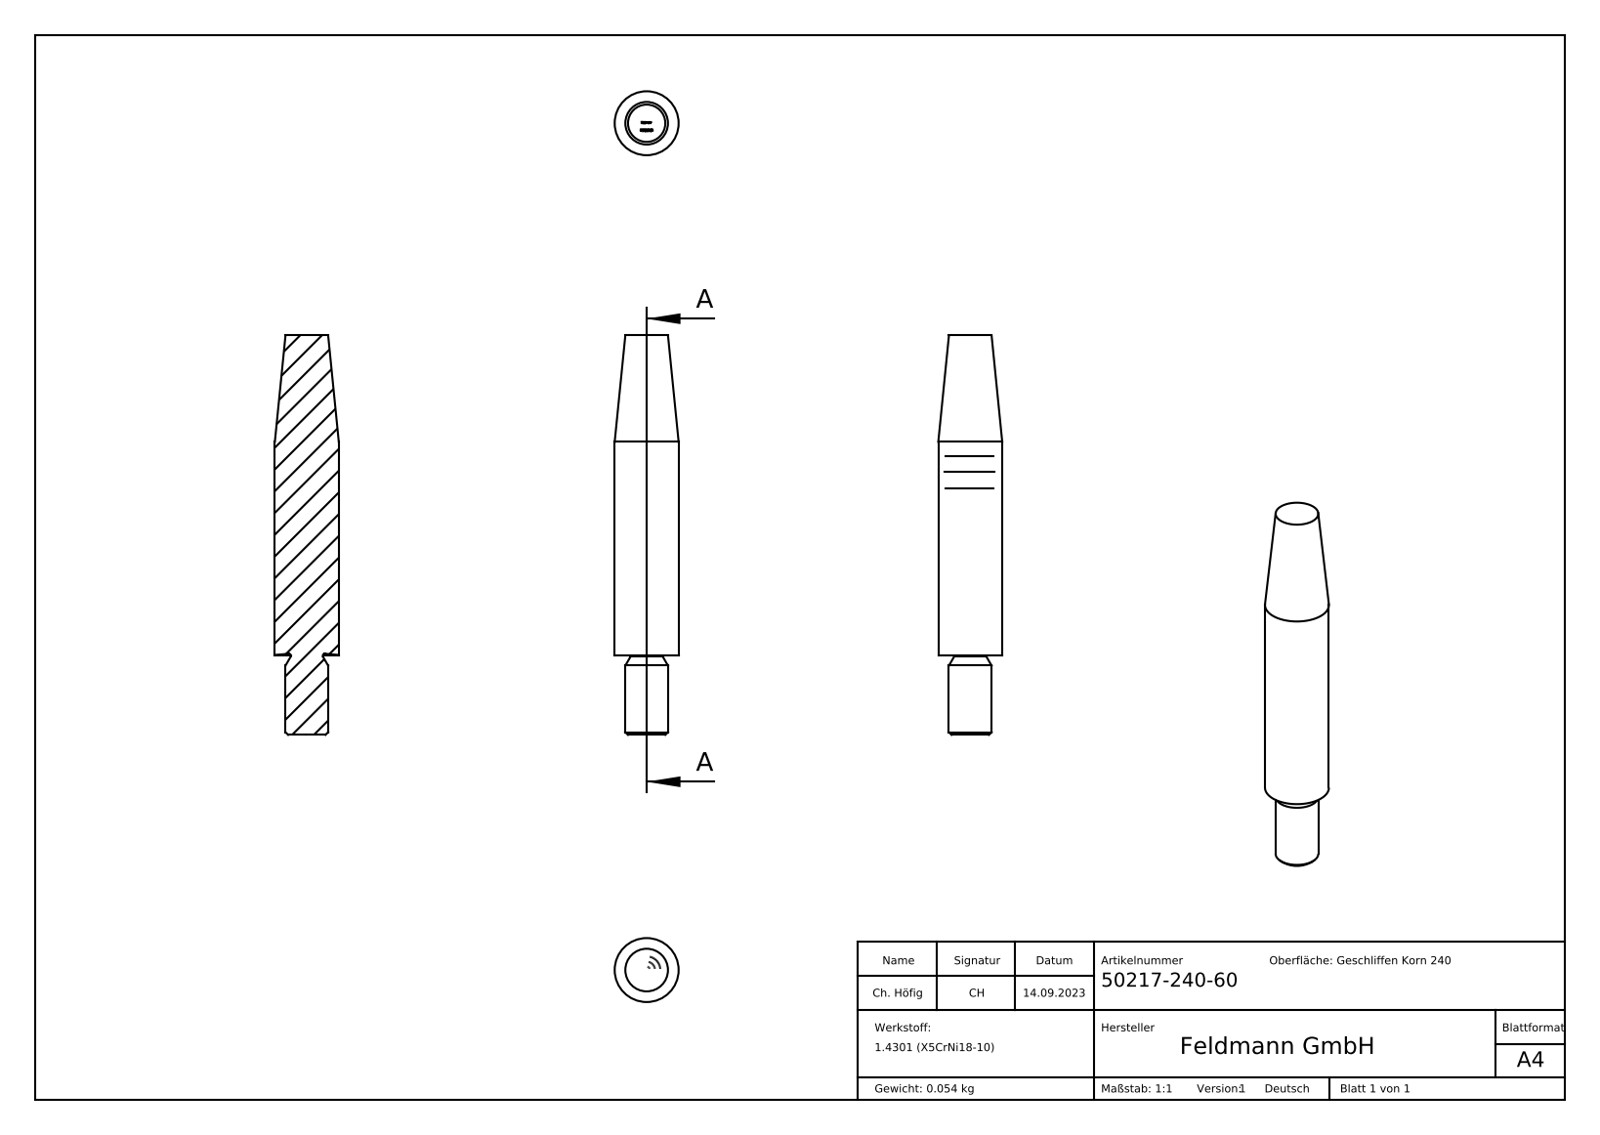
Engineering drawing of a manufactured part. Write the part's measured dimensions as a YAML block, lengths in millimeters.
part_name: "50217-240-60"
step_written_by: "SolidWorks 2018 (CONFIG_CONTROL_DESIGN)"
units: millimeters
bodies: {solids: 1, faces: 246, planar: 145, cylindrical: 2, other: 99}
overall_size: [75, 12, 12]
volume: 6832
surface_area: 2696
round_bosses_or_shafts:
  - {diameter: 12, count: 1}
  - {diameter: 8, count: 1}
face_to_face_distances: [75, 74.9, 0.33, 0.54, 1.44, 0.94, 0.79, 0.59, 1.33, 0.91]
